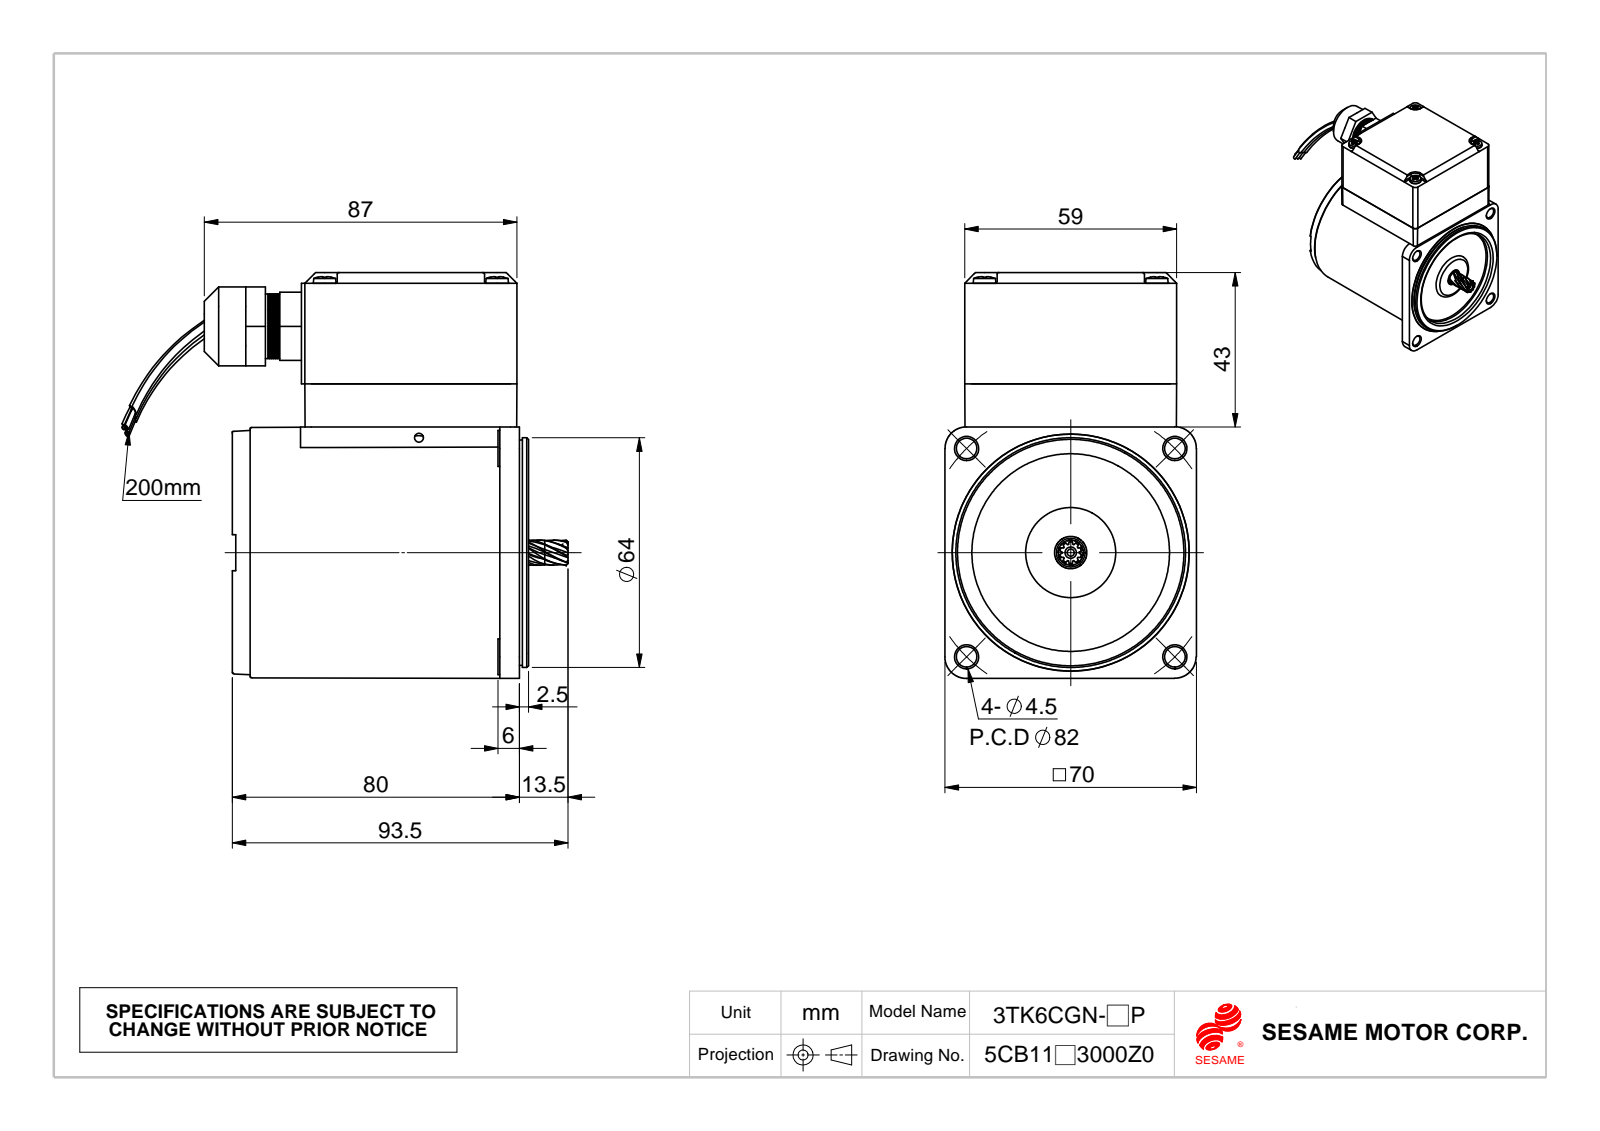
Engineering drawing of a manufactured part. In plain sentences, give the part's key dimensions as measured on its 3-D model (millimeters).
The part is named "M315Ts_2車工; Ts下墊片; C364_車工(成品); 15GN_0.成品 (+1 more)". Its 3-D file was written by "SolidWorks 2010 (CONFIG_CONTROL_DESIGN)". It is 14 solids with 2475 faces: 213 planar, 808 cylindrical and 1454 other. Overall it measures 124.22 by 113 by 70 millimeters. Its volume is 469 351 cubic millimeters and its surface area 74 079 square millimeters. Round holes: 4 of diameter 3.3, 4 of diameter 3.5, 4 of diameter 3.9, 4 of diameter 4.3, 4 of diameter 5.75, 1 of diameter 2, 1 of diameter 2.5, 1 of diameter 9, 1 of diameter 11, 1 of diameter 12, 1 of diameter 14.5, 1 of diameter 18. Round bosses or shafts: 5 of diameter 10, 4 of diameter 6.3, 4 of diameter 3, 1 of diameter 63.93, 1 of diameter 62.73, 1 of diameter 57.42, 1 of diameter 57.2, 1 of diameter 22. Partial cylindrical surfaces (rounded edges, fillets, slot ends): 12 of radius 2, 8 of radius 0.5, 6 of radius 4, 4 of radius 1.5, 4 of radius 3, 4 of radius 3.5, 4 of radius 6, 1 of radius 34.25. The main face-to-face distances are 12, 0.75, 77.4, 31, 1.5, 77.5, 43, 59, 75.89, 1.51. The hole center spacings are 41.01, 48, 58, 11.67, 12.35, 12.7, 24.93, 25.
